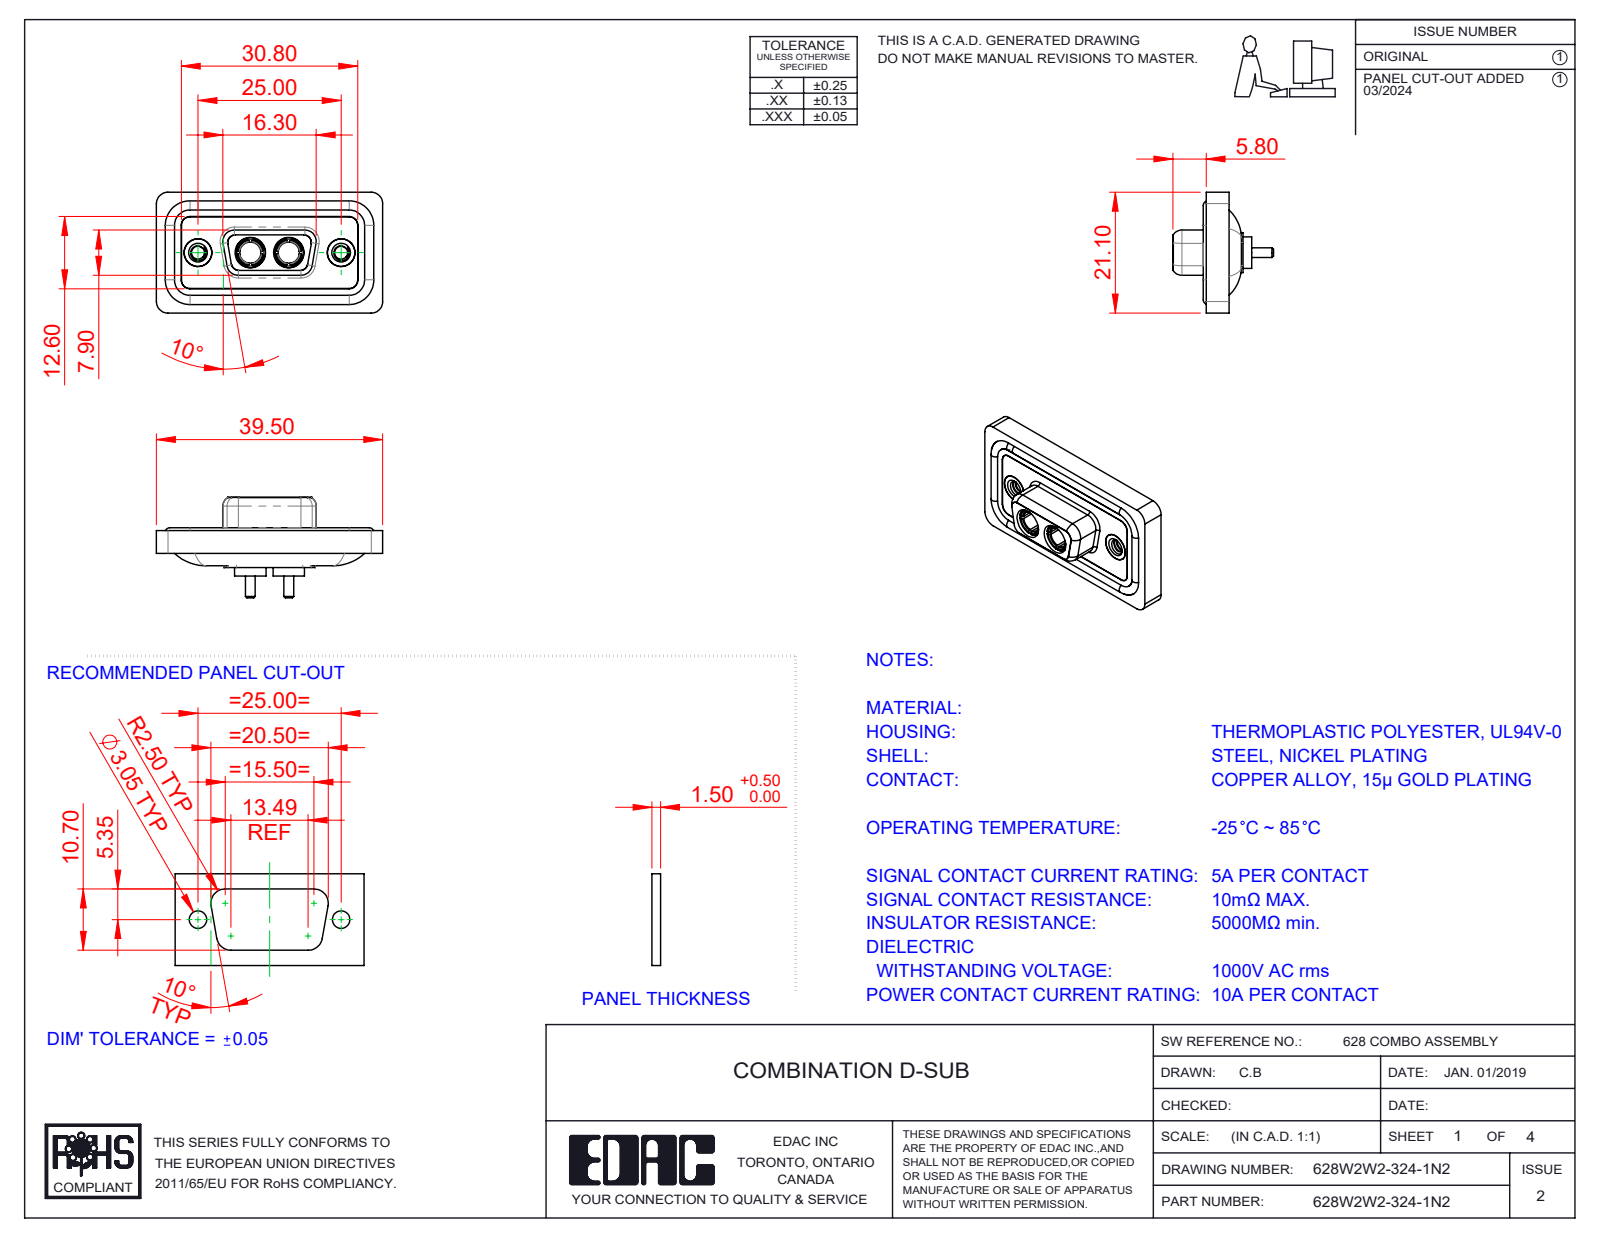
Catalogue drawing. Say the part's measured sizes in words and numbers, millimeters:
The part is named "628Combo Housing_2W2; 628W2W2-324-1N2; 628Combo Shell Front_09 Contacts; 628Combo Shell Rear_09 Contacts (+3 more)". Its 3-D file was written by "SolidWorks 2023 (CONFIG_CONTROL_DESIGN)". It is 11 solids with 534 faces: 163 planar, 234 cylindrical and 137 other. Overall it measures 39.5 by 21.1 by 17.55 millimeters. Its volume is 4 683 cubic millimeters and its surface area 7 611 square millimeters. Round holes: 4 of diameter 4.85, 2 of diameter 2.26, 2 of diameter 3.7, 2 of diameter 4, 2 of diameter 4.05, 2 of diameter 5, 2 of diameter 5.3. Round bosses or shafts: 4 of diameter 1.6, 2 of diameter 5.5, 2 of diameter 5.2, 2 of diameter 4.96, 2 of diameter 4.95, 2 of diameter 4.8, 2 of diameter 4.75, 2 of diameter 3.75. Partial cylindrical surfaces (rounded edges, fillets, slot ends): 22 of radius 1.5, 18 of radius 2, 8 of radius 1.35, 8 of radius 1.6, 4 of radius 0.25, 4 of radius 0.5, 4 of radius 0.6, 4 of radius 0.65. The main face-to-face distances are 0.4, 1.8, 1.1, 2.9, 0.5, 1.6, 5.65, 1.5, 7.45, 5.35. The hole center spacings are 9.14, 15.86, 6.72, 25.
